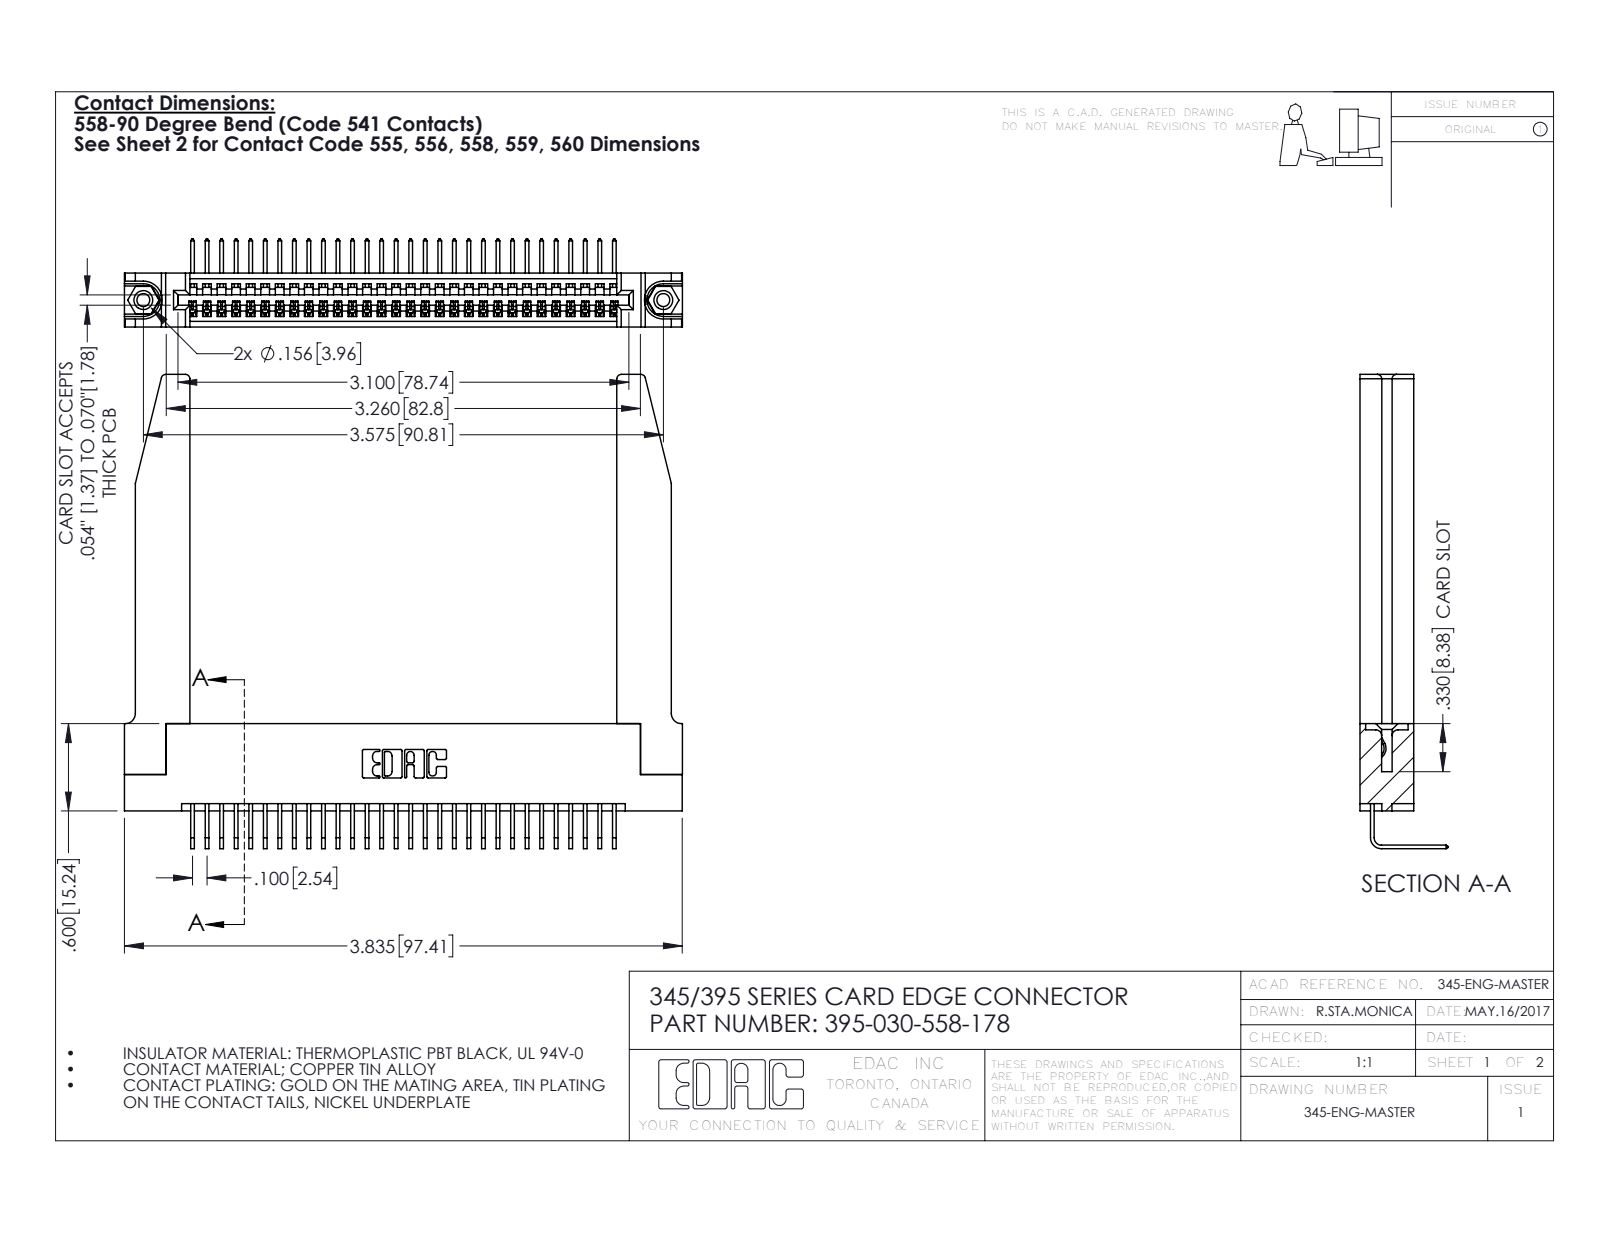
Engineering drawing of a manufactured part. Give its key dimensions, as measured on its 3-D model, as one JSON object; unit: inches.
{"part_name": "345 Part_Flush Mounting Lugs - 0.156 Dia-TH; 345-250-001_345-250-001-102; 345-220-078_345-220-078; 395-030-558-178 (+1 more)", "step_written_by": "SolidWorks 2016 (CONFIG_CONTROL_DESIGN)", "units": "inches", "bodies": {"solids": 35, "faces": 2160, "planar": 1482, "cylindrical": 626, "other": 52}, "overall_size": [3.836, 3.259, 0.605], "volume_in3": 1.039, "surface_area_in2": 30.33, "round_holes": [[0.089, 2], [0.125, 2], [0.156, 2], [0.064, 1]], "round_bosses_or_shafts": [[0.155, 2]], "partial_cylinders_radius": [[0.006, 60], [0.01, 22], [0.03, 8], [0.007, 6], [0.031, 6], [0.026, 3], [0.031, 2], [0.04, 2]], "face_to_face_distances": [0.37, 0.072, 0.298, 0.2, 0.098, 0.272, 0.025, 0.148, 0.15, 0.225], "hole_center_spacings": [0.27, 3.34, 3.575]}
